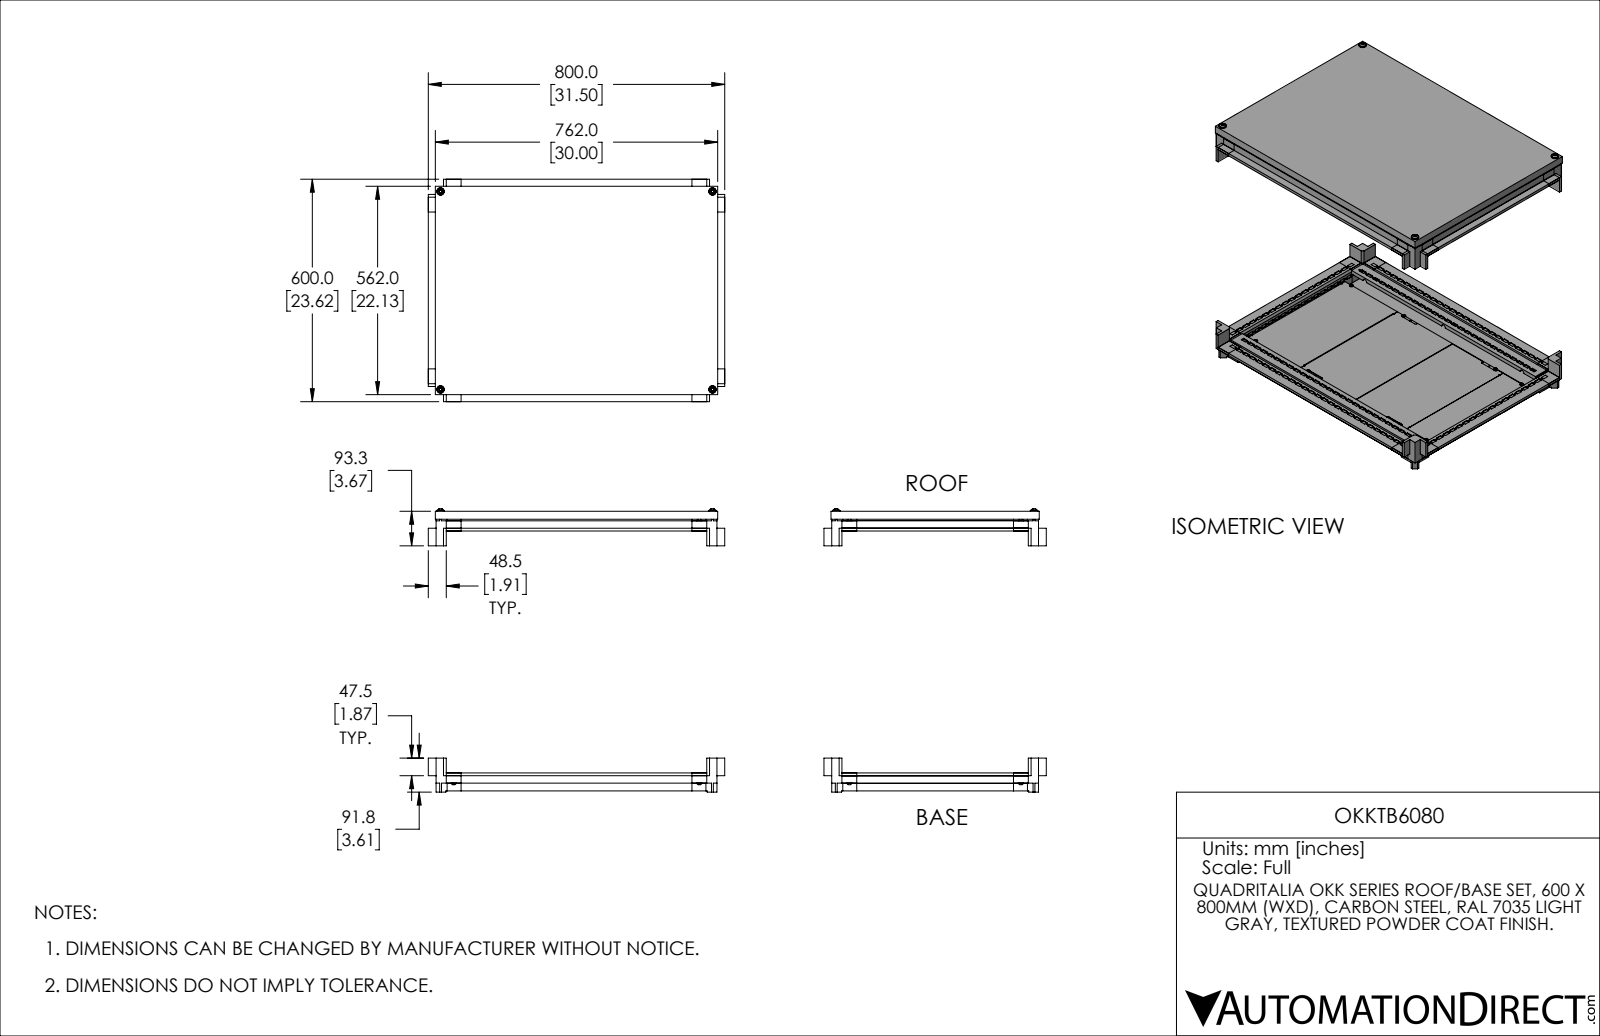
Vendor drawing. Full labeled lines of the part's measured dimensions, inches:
Part name (STEP PRODUCT): OKKTB6080
STEP written by: SolidWorks 2021 (AUTOMOTIVE_DESIGN)
Units: inches
Bodies: 62 solids, 4787 faces (3654 planar, 962 cylindrical, 171 other)
Overall size (bounding box): 31.496 × 30.066 × 23.622
Volume: 504.3 in³ · Surface area: 5 198 in²
Round holes (diameter × count): ⌀0.167 ×284, ⌀0.354 ×11, ⌀0.154 ×8, ⌀0.194 ×3, ⌀0.323 ×3
Round bosses / shafts (diameter × count): ⌀0.551 ×11, ⌀0.394 ×11, ⌀0.315 ×11, ⌀0.197 ×8, ⌀0.787 ×4, ⌀0.472 ×4, ⌀0.236 ×4, ⌀0.276 ×1
Partial cylindrical surfaces — rounded edges, fillets, slot ends (radius × count): R0.02 ×264, R0.039 ×24, R0.01 ×16, R0.138 ×12, R0.177 ×12, R0.03 ×9, R0.217 ×6, R0.276 ×3
Main face-to-face distances: 0.059, 28.767, 28.826, 0.787, 0.098, 1.083, 0.295, 0.689, 1.102, 0.984
Hole centre spacings: 0.984, 1.969, 2.953, 3.937, 4.921, 5.906, 6.89, 7.874
